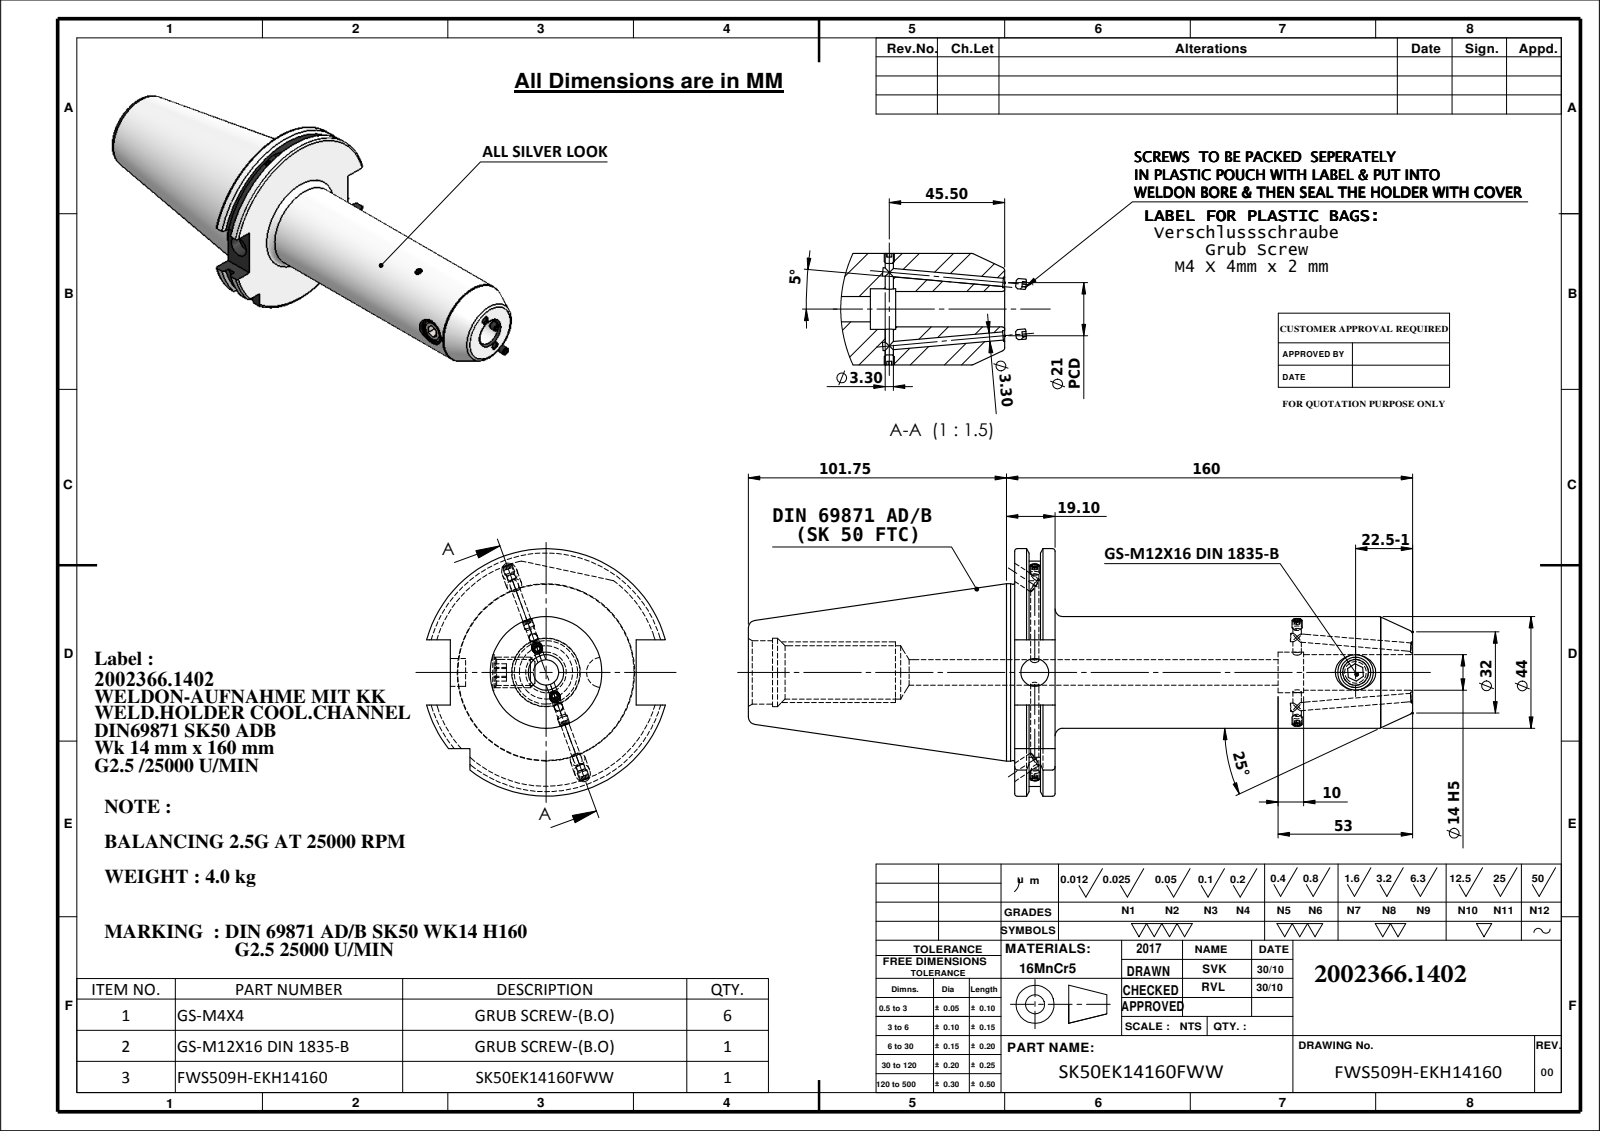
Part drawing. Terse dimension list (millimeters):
name: 91506-WK214160; Copy of M4X4_DIN 913 - M4 x 4-N; M12X16_ISO 4026 - M12 x 12-N; SK50EK14160FWW
written by: SolidWorks 2009 (CONFIG_CONTROL_DESIGN)
unit: mm
bodies: 8 solids, 252 faces (93 planar, 83 cylindrical, 76 other)
size: 270.28 × 97.5 × 94.05
volume: 526 643 mm³; area: 69 947 mm²
holes: 4× ⌀3.3, 2× ⌀4.2, 2× ⌀6, 2× ⌀14, 1× ⌀10, 1× ⌀10.2, 1× ⌀11, 1× ⌀16, 1× ⌀21, 1× ⌀25, 1× ⌀27
bosses: 6× ⌀4, 1× ⌀69.85, 1× ⌀69.45, 1× ⌀44, 1× ⌀12
rounds: 1× R44.9, 1× R48.75
face distances: 15.9, 10.15, 5.75, 5.66, 4.49, 10.24, 156.8, 151.14, 146.65, 140.9
hole spacings: 103.4, 126.4
